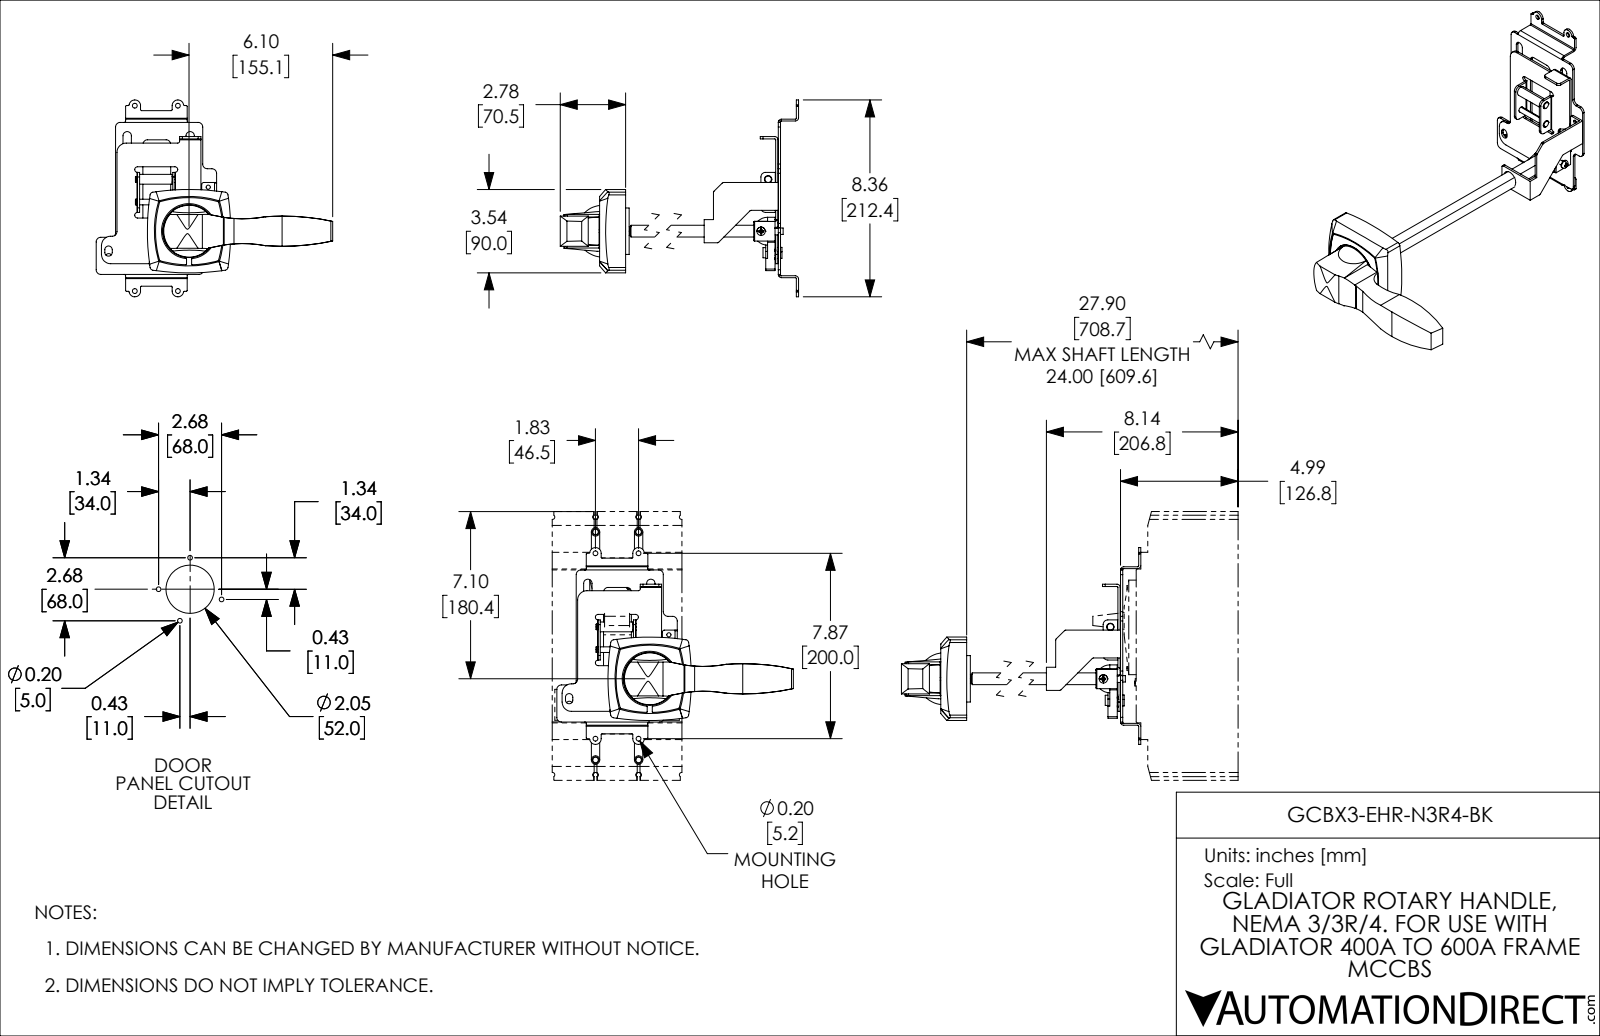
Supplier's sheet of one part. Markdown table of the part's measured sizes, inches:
| quantity | value |
| --- | --- |
| part name | GCBX3-EHR-N3R4-BK |
| STEP written by | SolidWorks 2021 (CONFIG_CONTROL_DESIGN) |
| units | inches |
| bodies | 14 solids, 582 faces (232 planar, 290 cylindrical, 60 other) |
| overall size | 15.102 × 10.054 × 8.362 |
| volume | 31.24 in³ |
| surface area | 230.4 in² |
| round holes (diameter × count) | 0.197 × 4, 0.205 × 4, 0.315 × 3, 0.138 × 2, 0.157 × 2, 0.177 × 2, 0.244 × 2, 0.276 × 2, 0.161 × 1, 0.169 × 1, 0.209 × 1, 0.224 × 1 |
| round bosses / shafts (diameter × count) | 0.197 × 3, 0.276 × 2, 0.236 × 2, 0.118 × 2, 2.343 × 1, 1.969 × 1, 0.472 × 1, 0.465 × 1 |
| partial cylindrical surfaces (radius × count) | 0.039 × 25, 0.197 × 21, 0.02 × 16, 0.118 × 11, 0.079 × 9, 0.059 × 8, 0.138 × 8, 0.394 × 5 |
| main face-to-face distances | 0.091, 0.11, 0.02, 0.201, 0.5, 11.622, 11.531, 11.512, 11.421, 0.919 |
| hole center spacings | 1.339, 0.051, 1.263, 1.299, 1.3, 1.338, 1.407, 1.407 |
